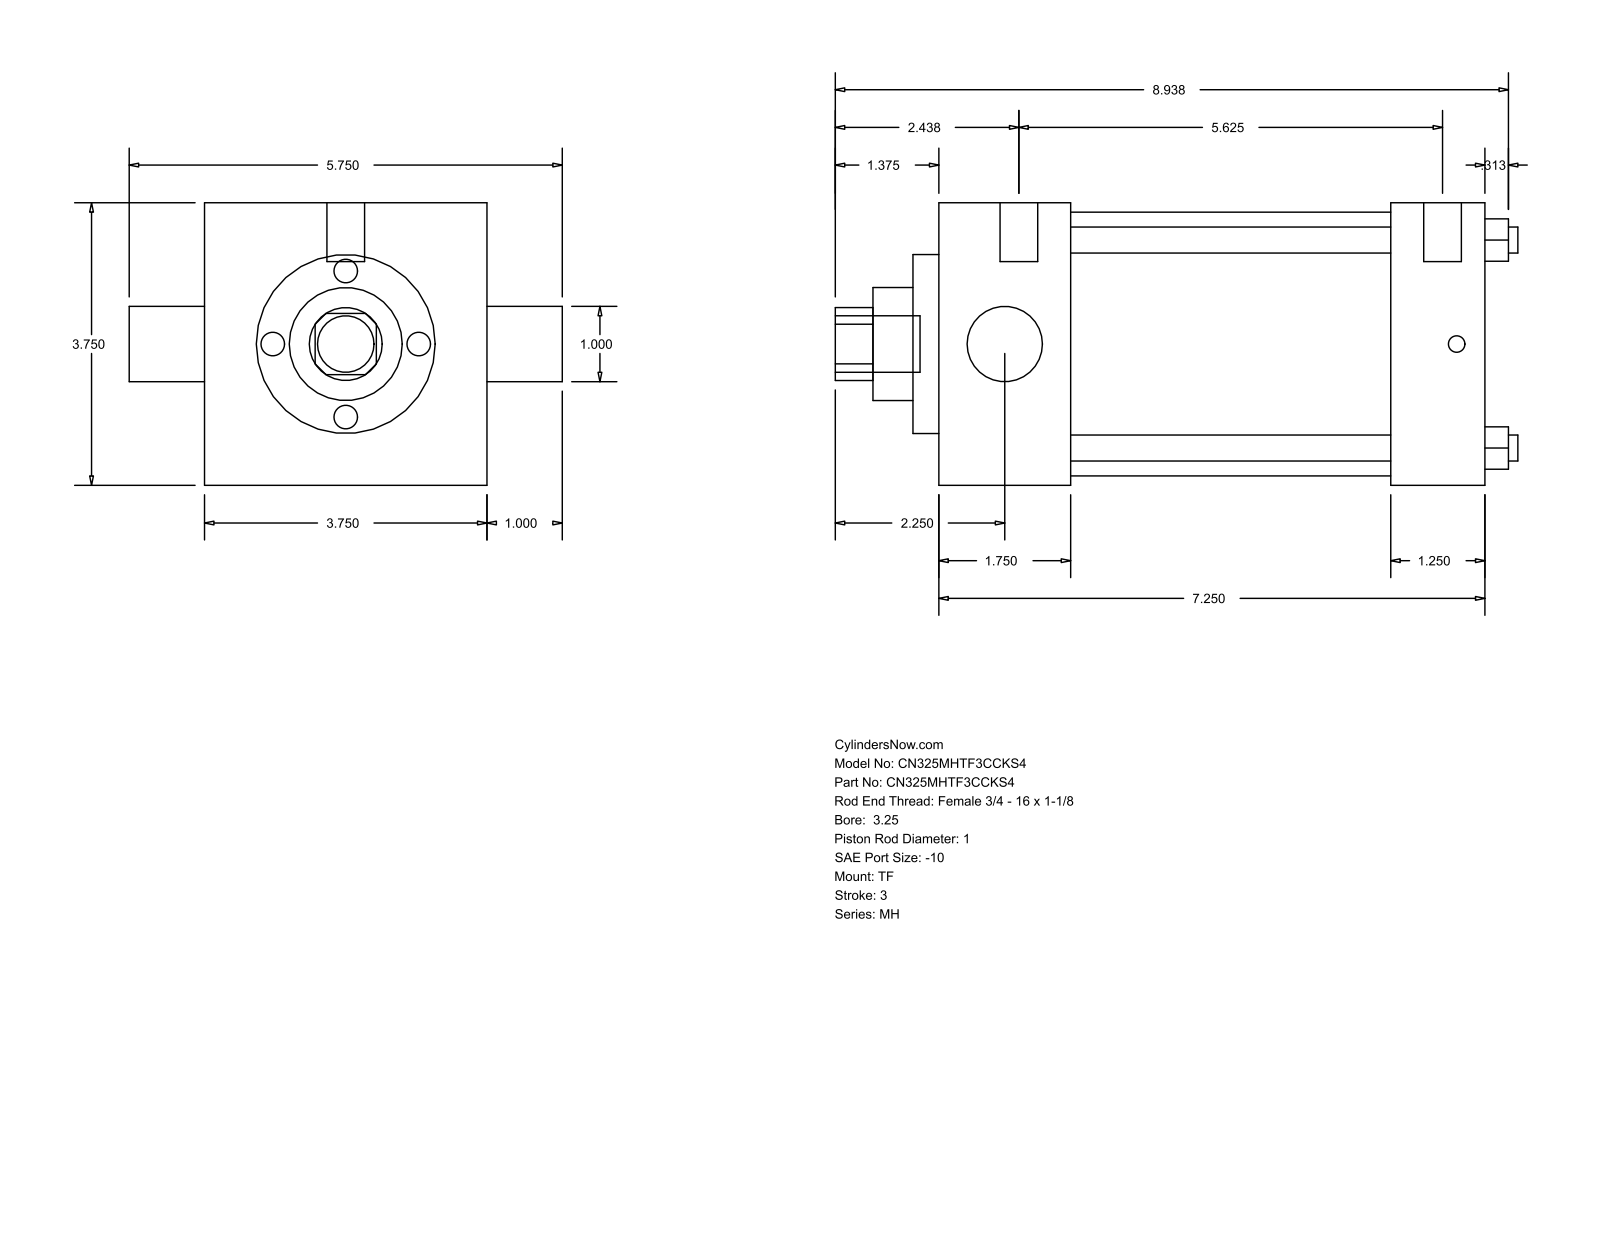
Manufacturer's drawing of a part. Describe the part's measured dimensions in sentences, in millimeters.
The part is named "MH_TF__0325_1". Its 3-D file was written by "GSSL Pune (CONFIG_CONTROL_DESIGN)". It is 0 solids with 86 faces: 61 planar, 25 cylindrical and 0 other. Overall it measures 230.19 by 146.05 by 95.25 millimeters. Round holes: 4 of diameter 8.76, 2 of diameter 25.4, 1 of diameter 38.1, 1 of diameter 60.33, 1 of diameter 88.9. Round bosses or shafts: 3 of diameter 5.56, 2 of diameter 12.7, 1 of diameter 19.05. Partial cylindrical surfaces (rounded edges, fillets, slot ends): 1 of radius 12.29. The main face-to-face distances are 95.24, 184.15, 44.46, 152.4, 107.94, 139.69, 31.75, 8.73, 53.19, 161.13. The hole center spacings are 49.57, 70.1, 99.14.
